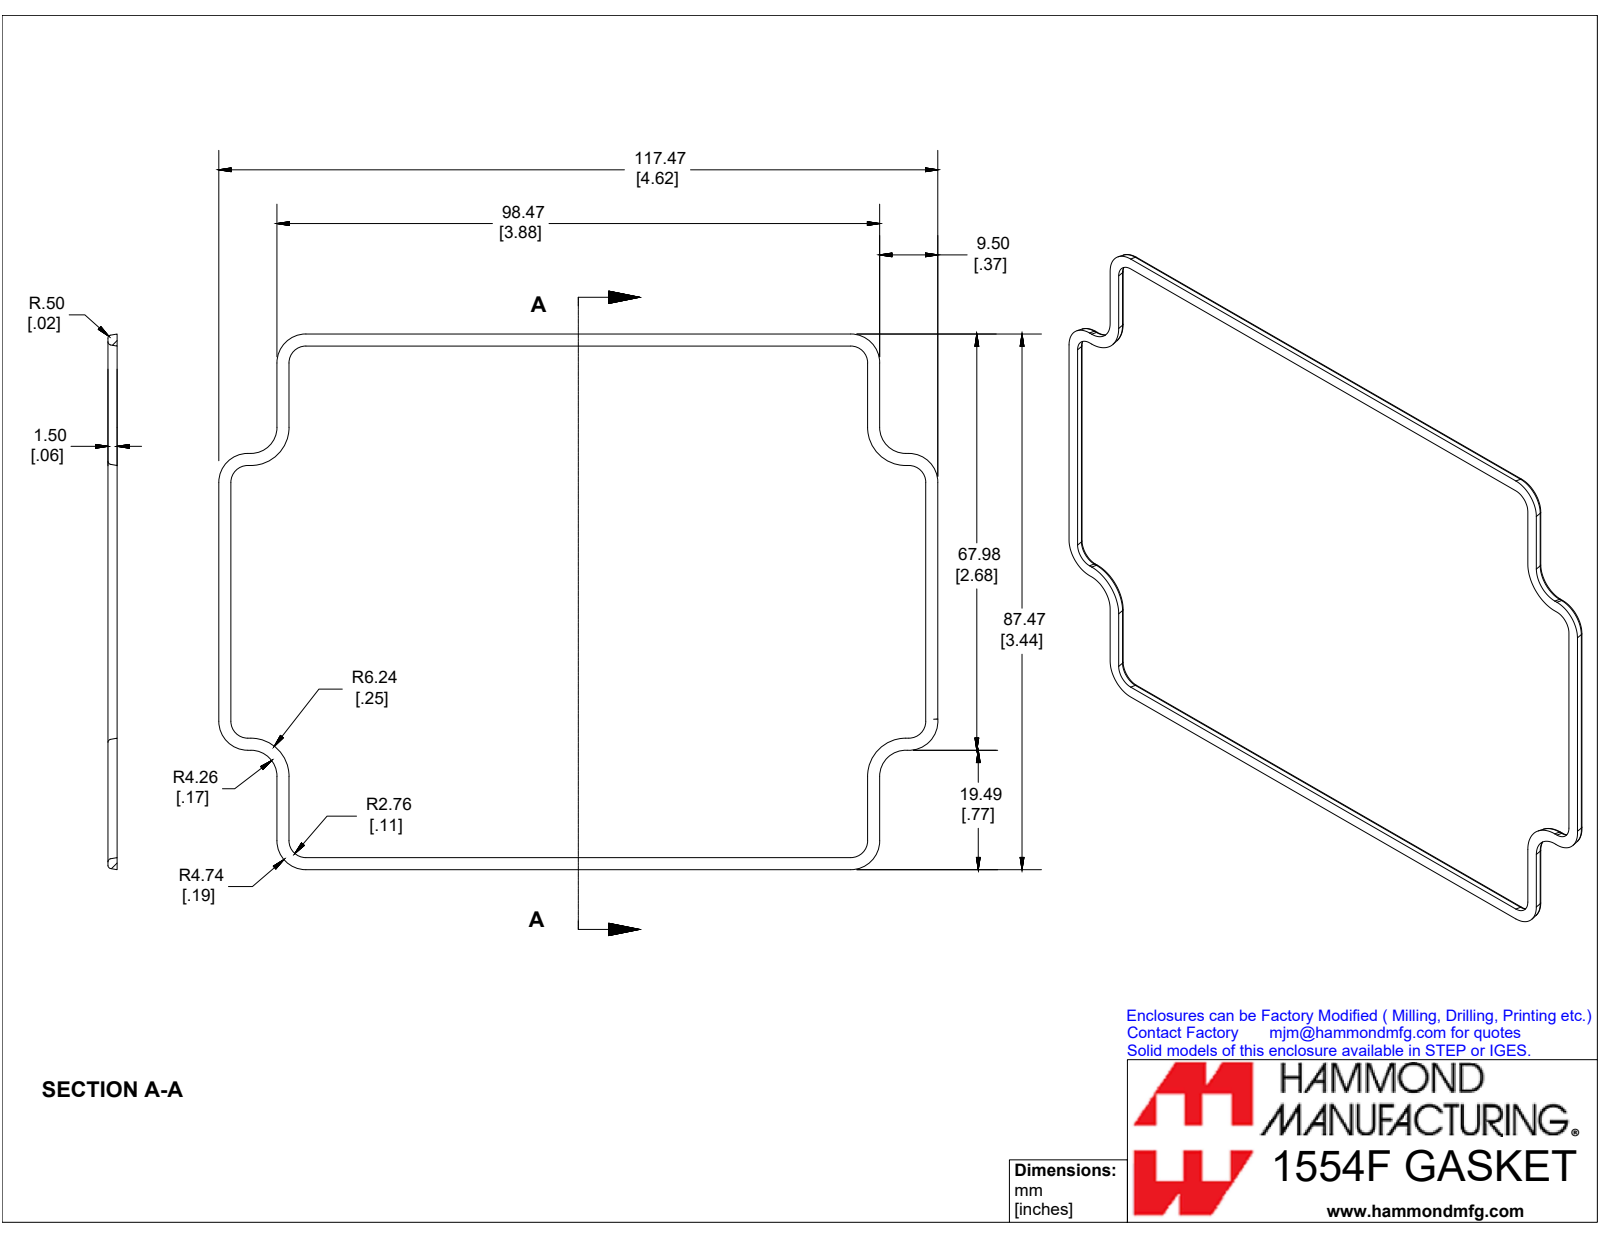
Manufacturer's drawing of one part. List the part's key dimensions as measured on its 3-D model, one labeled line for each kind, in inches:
Part name (STEP PRODUCT): 1554FGASKET
STEP written by: SolidWorks 2019 (CONFIG_CONTROL_DESIGN)
Units: inches
Bodies: 1 solid, 96 faces (25 planar, 23 cylindrical, 48 other)
Overall size (bounding box): 4.625 × 3.444 × 0.059
Volume: 0.058 in³ · Surface area: 3.64 in²
Partial cylindrical surfaces — rounded edges, fillets, slot ends (radius × count): R0.02 ×16
Main face-to-face distances: 0.059, 3.316, 3.315, 0.369, 4.111, 4.479, 3.742, 2.559, 0.756, 0.756
